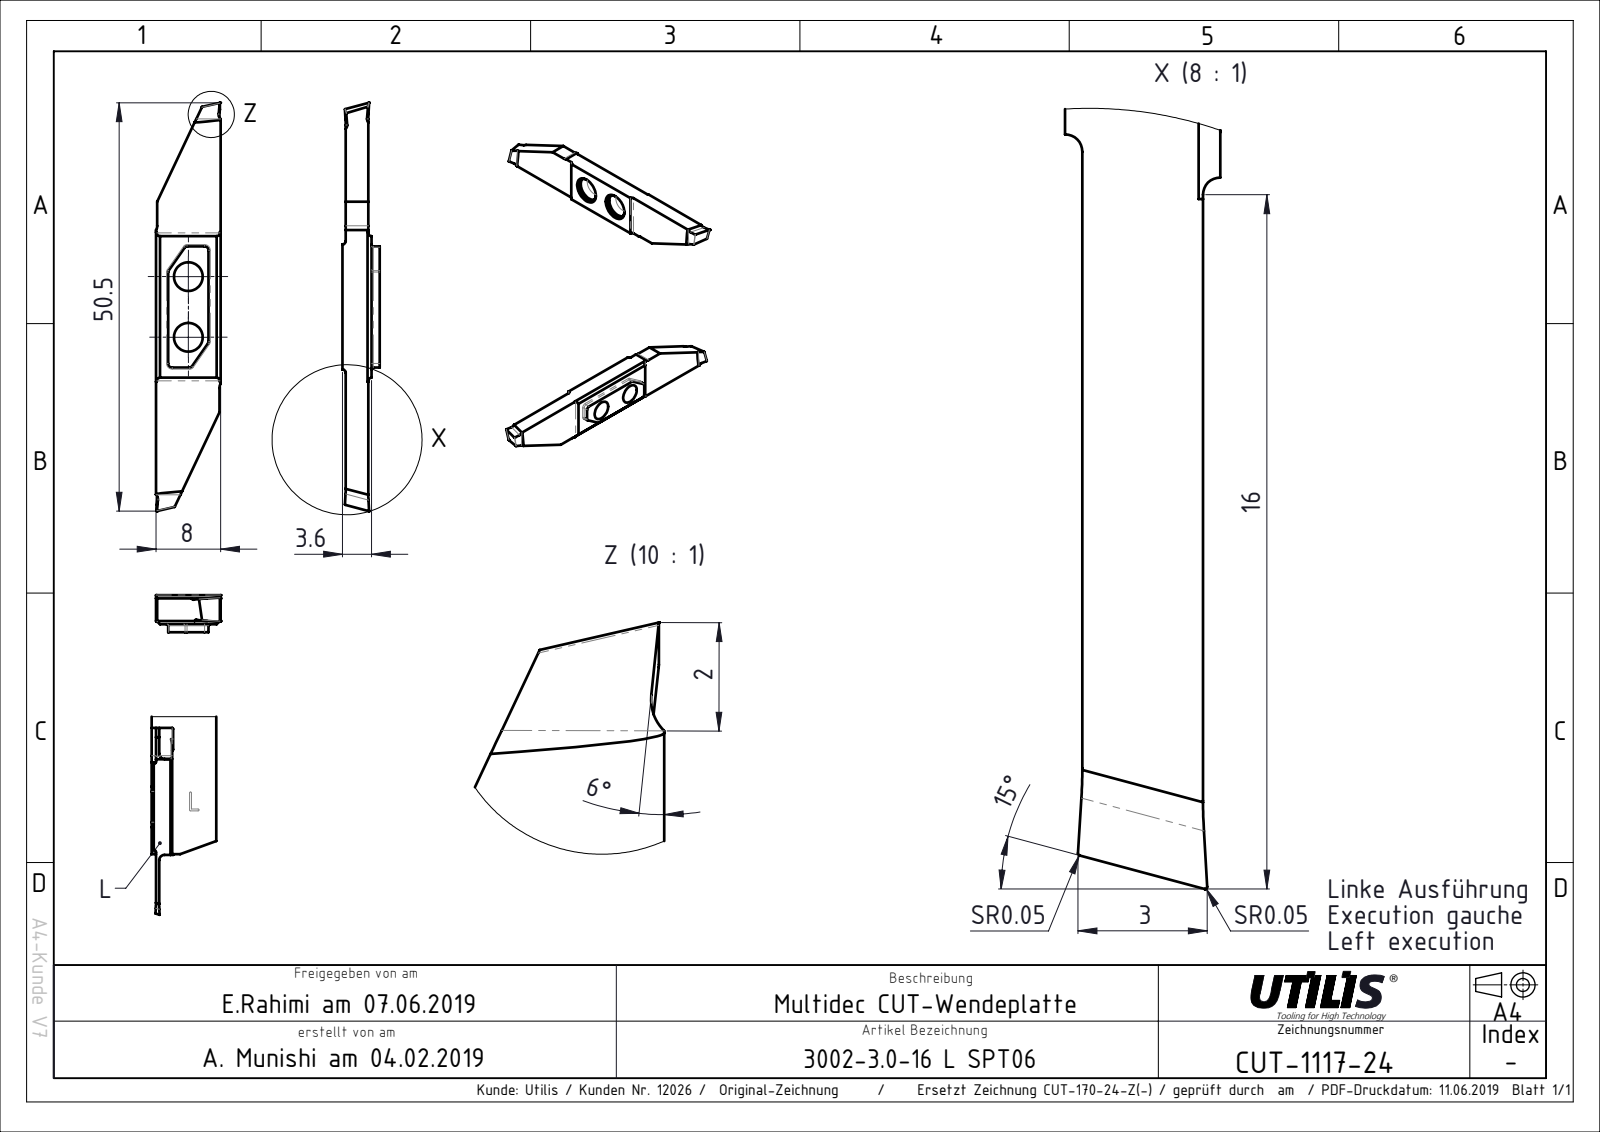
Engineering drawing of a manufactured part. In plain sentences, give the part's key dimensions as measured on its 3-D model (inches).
The part is named "CUT-1117; ASME Y14.5". Its 3-D file was written by "FormatWorks Professional (AP242_MANAGED_MODEL_BASED_3D_ENGINEERING_MIM_LF)". It is 1 solid with 42 faces: 26 planar, 16 cylindrical and 0 other. Overall it measures 1.988 by 0.315 by 0.142 inches. Its volume is 0.058 cubic inches and its surface area 1.578 square inches. Round holes: 2 of diameter 0.14. Partial cylindrical surfaces (rounded edges, fillets, slot ends): 4 of radius 0.016, 2 of radius 0.039. The main face-to-face distances are 0.016, 0.126, 0.11, 0.142, 0.315, 0.712, 0.309, 0.303, 0.059, 0.669. The hole center spacings are 0.295.
